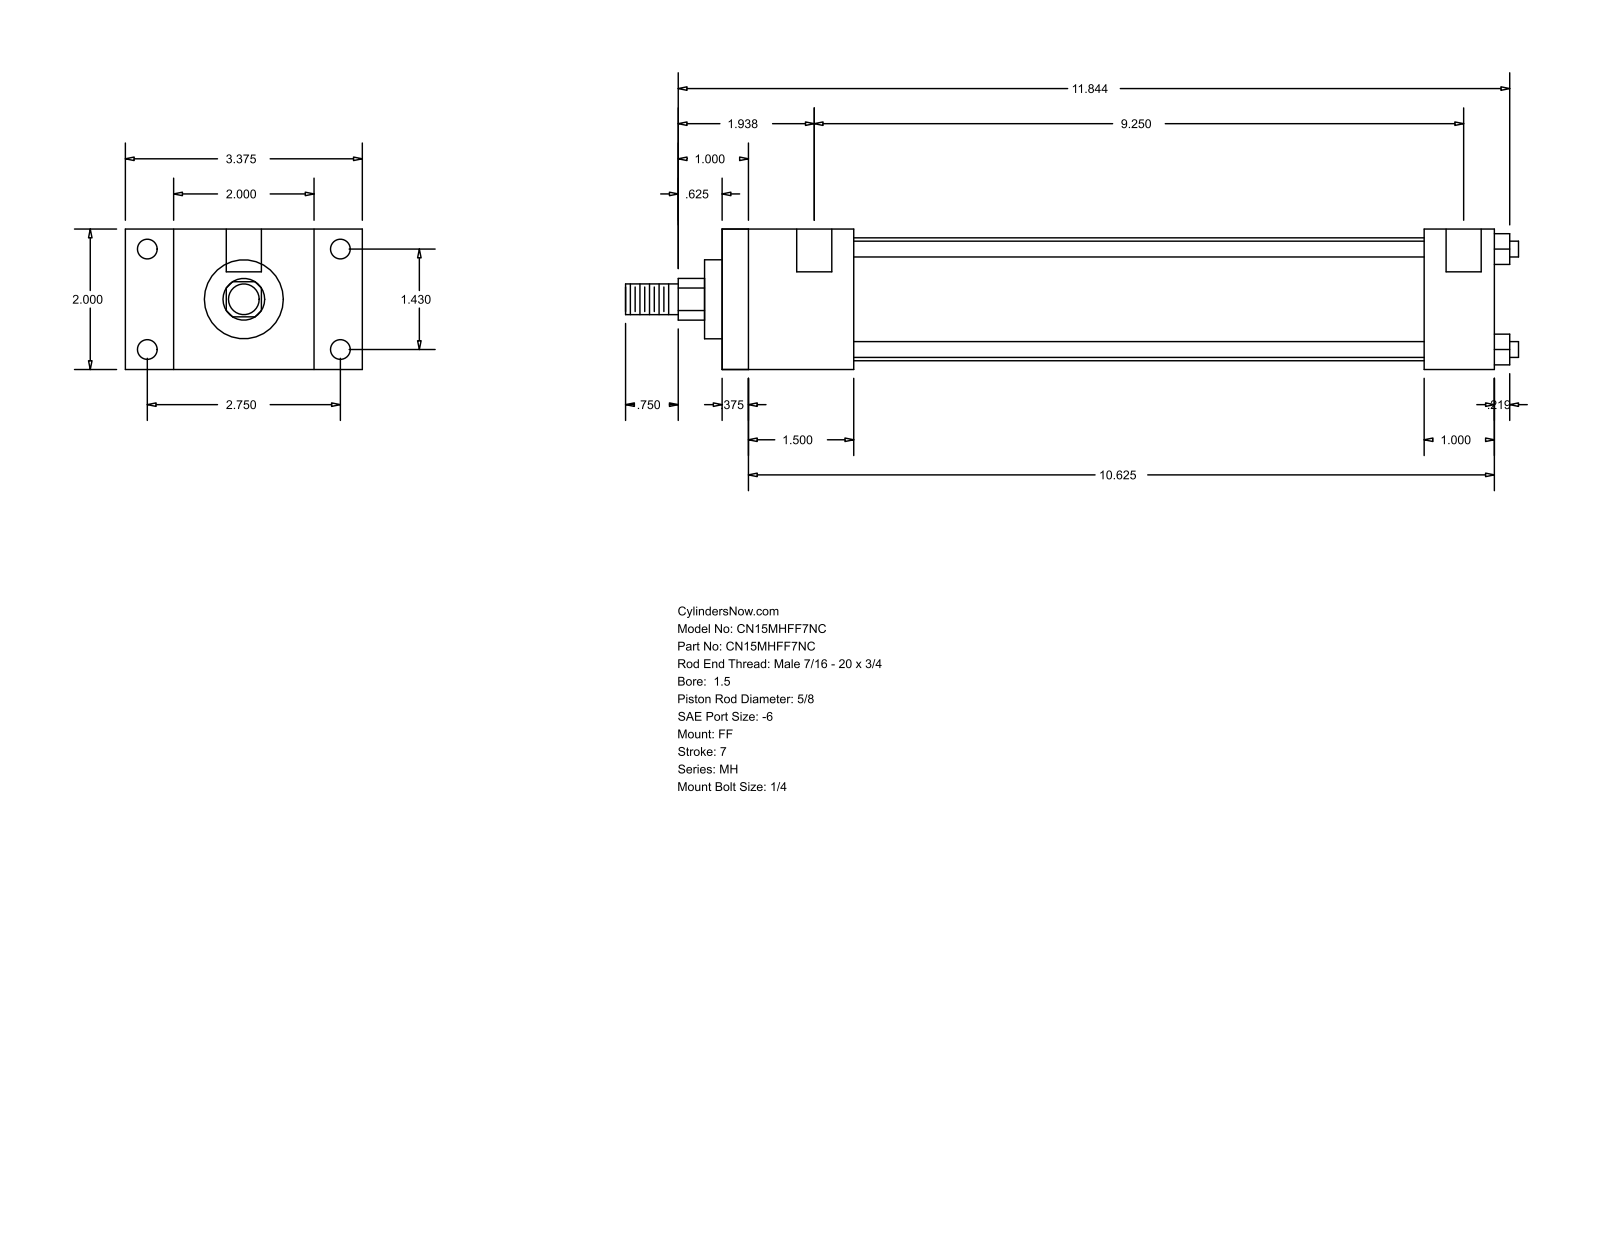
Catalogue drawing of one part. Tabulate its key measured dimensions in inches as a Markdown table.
| quantity | value |
| --- | --- |
| part name | MH_FF__0150_0.625 |
| STEP written by | GSSL Pune (CONFIG_CONTROL_DESIGN) |
| units | inches |
| bodies | 0 solids, 92 faces (64 planar, 28 cylindrical, 0 other) |
| overall size | 12.719 × 3.375 × 2 |
| round holes (diameter × count) | 0.219 × 4, 0.281 × 4, 0.5 × 2 |
| round bosses / shafts (diameter × count) | 0.225 × 4, 1.75 × 1, 1.125 × 1, 0.625 × 1, 0.437 × 1 |
| partial cylindrical surfaces (radius × count) | 0.297 × 1 |
| main face-to-face distances | 2, 11, 0.375, 10.625, 0.687, 2.687, 1.875, 1.5, 9.125, 10 |
| hole center spacings | 1.43, 2.75, 3.099, 9.375, 0.125, 9.25 |
